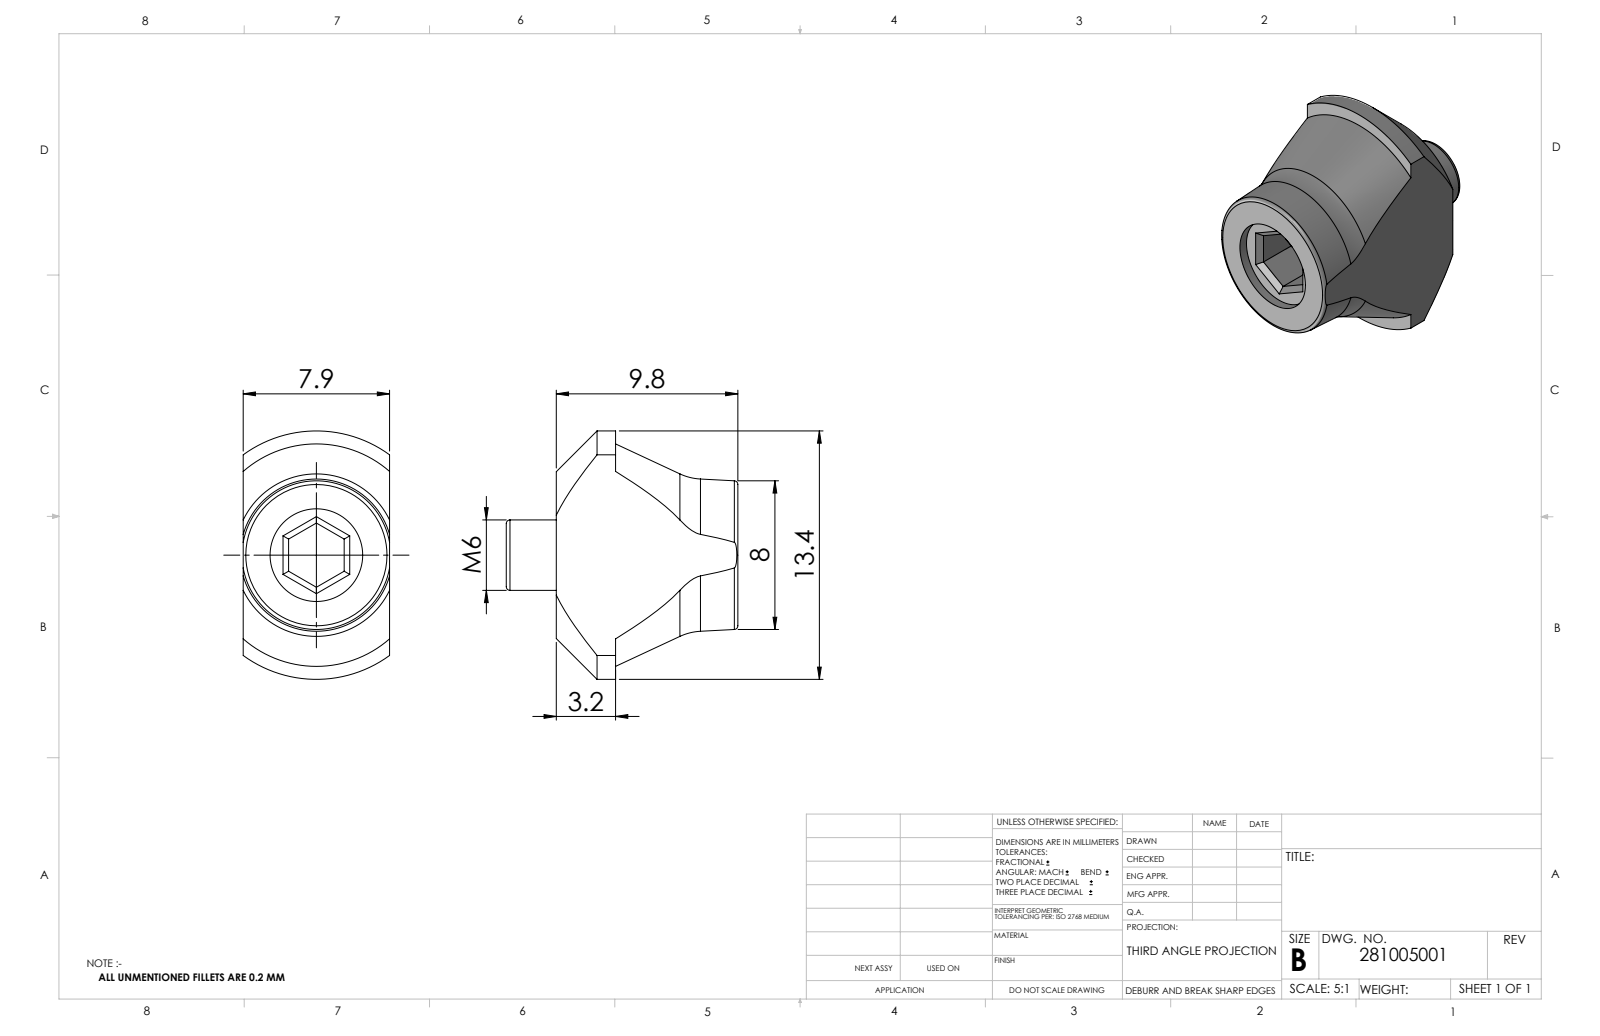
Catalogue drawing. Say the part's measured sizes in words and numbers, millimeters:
The part is named "281005001_c_1". Its 3-D file was written by "SolidWorks 2014 (CONFIG_CONTROL_DESIGN)". It is 2 solids with 46 faces: 21 planar, 8 cylindrical and 17 other. Overall it measures 13.4 by 12.5 by 7.9 millimeters. Its volume is 748 cubic millimeters and its surface area 838 square millimeters. Round holes: 1 of diameter 5. Round bosses or shafts: 1 of diameter 6, 1 of diameter 3.8. Partial cylindrical surfaces (rounded edges, fillets, slot ends): 1 of radius 6.7. The main face-to-face distances are 7.9, 9.8, 3, 3.2, 6.6, 2.45, 5.45, 2.7, 5.9, 12.5.
